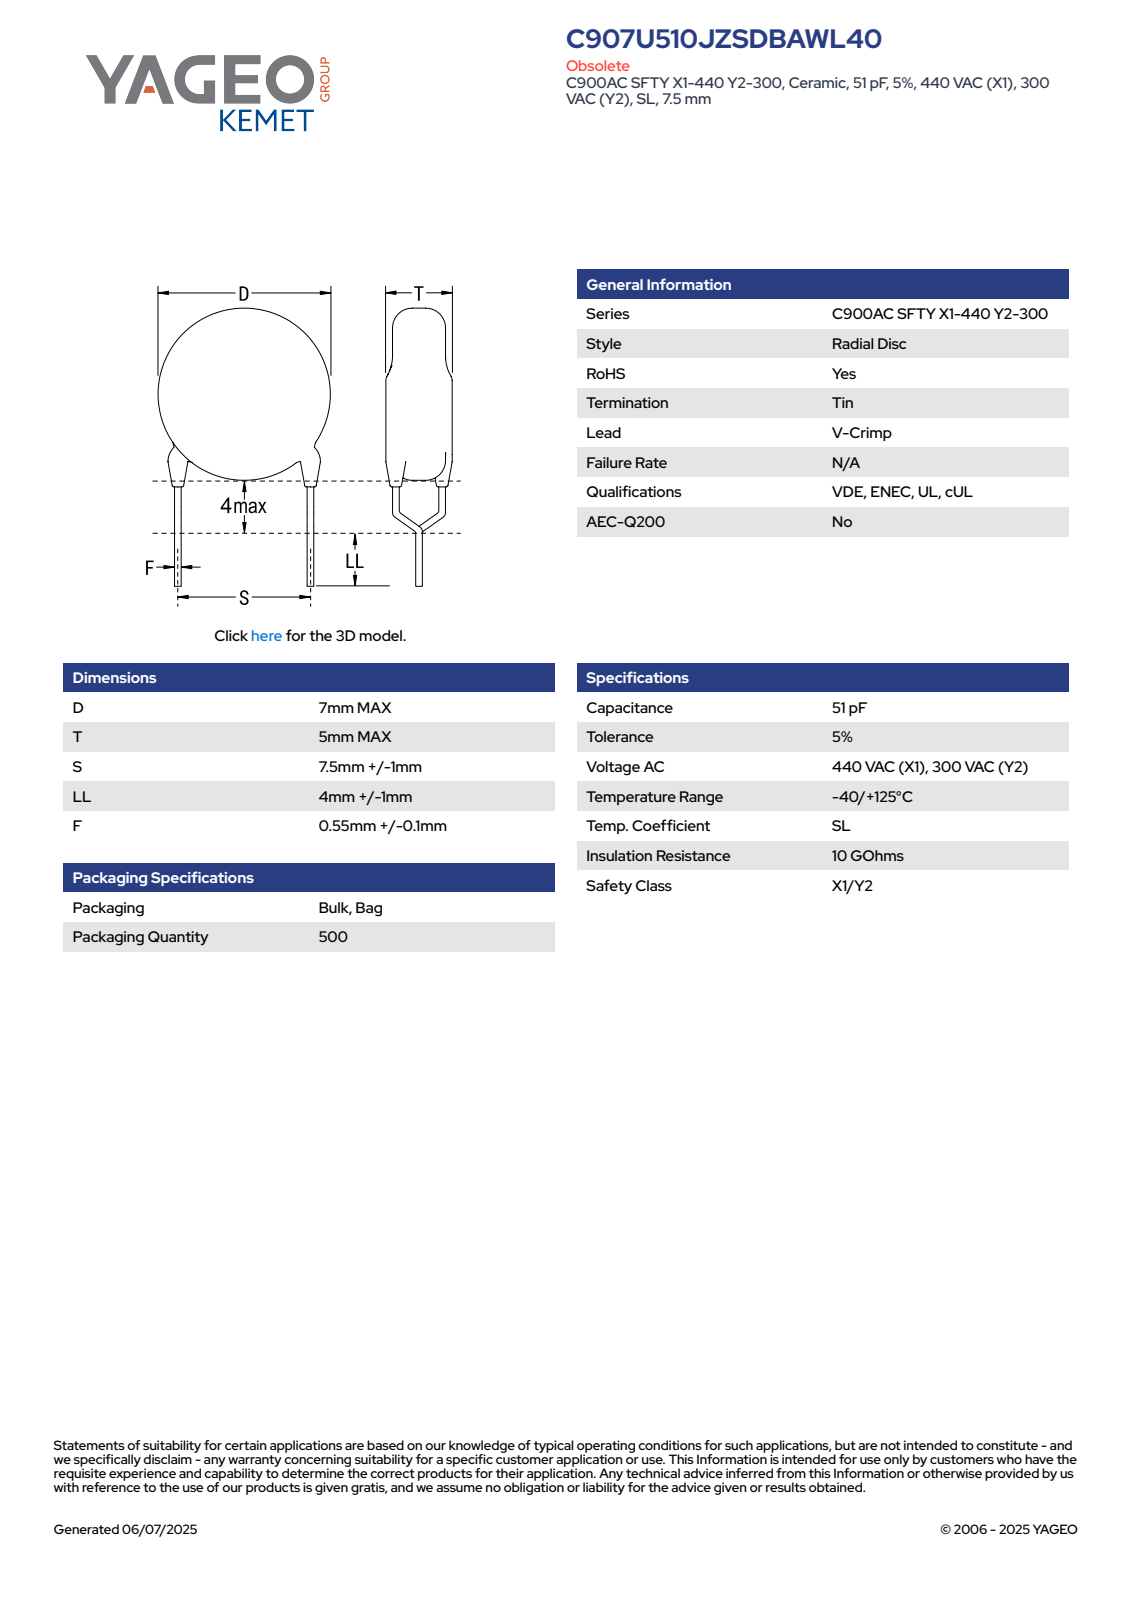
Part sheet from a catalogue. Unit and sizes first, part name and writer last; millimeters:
Units: millimetres
Overall size (bounding box): 15.8 × 8.15 × 5
Round bosses / shafts (diameter × count): ⌀0.65 ×6, ⌀7 ×1
Main face-to-face distances: 5, 7.9, 0.91, 12.75, 4.85, 11.84, 3.94, 3.71, 0.34, 1.87
Volume: 193 mm³ · Surface area: 220 mm²
Bodies: 5 solids, 93 faces (65 planar, 16 cylindrical, 12 other)
Part name (STEP PRODUCT): CCD_VCC900_D7T5S7.5LL5F0.65
STEP written by: SolidWorks 2014 (AUTOMOTIVE_DESIGN)
